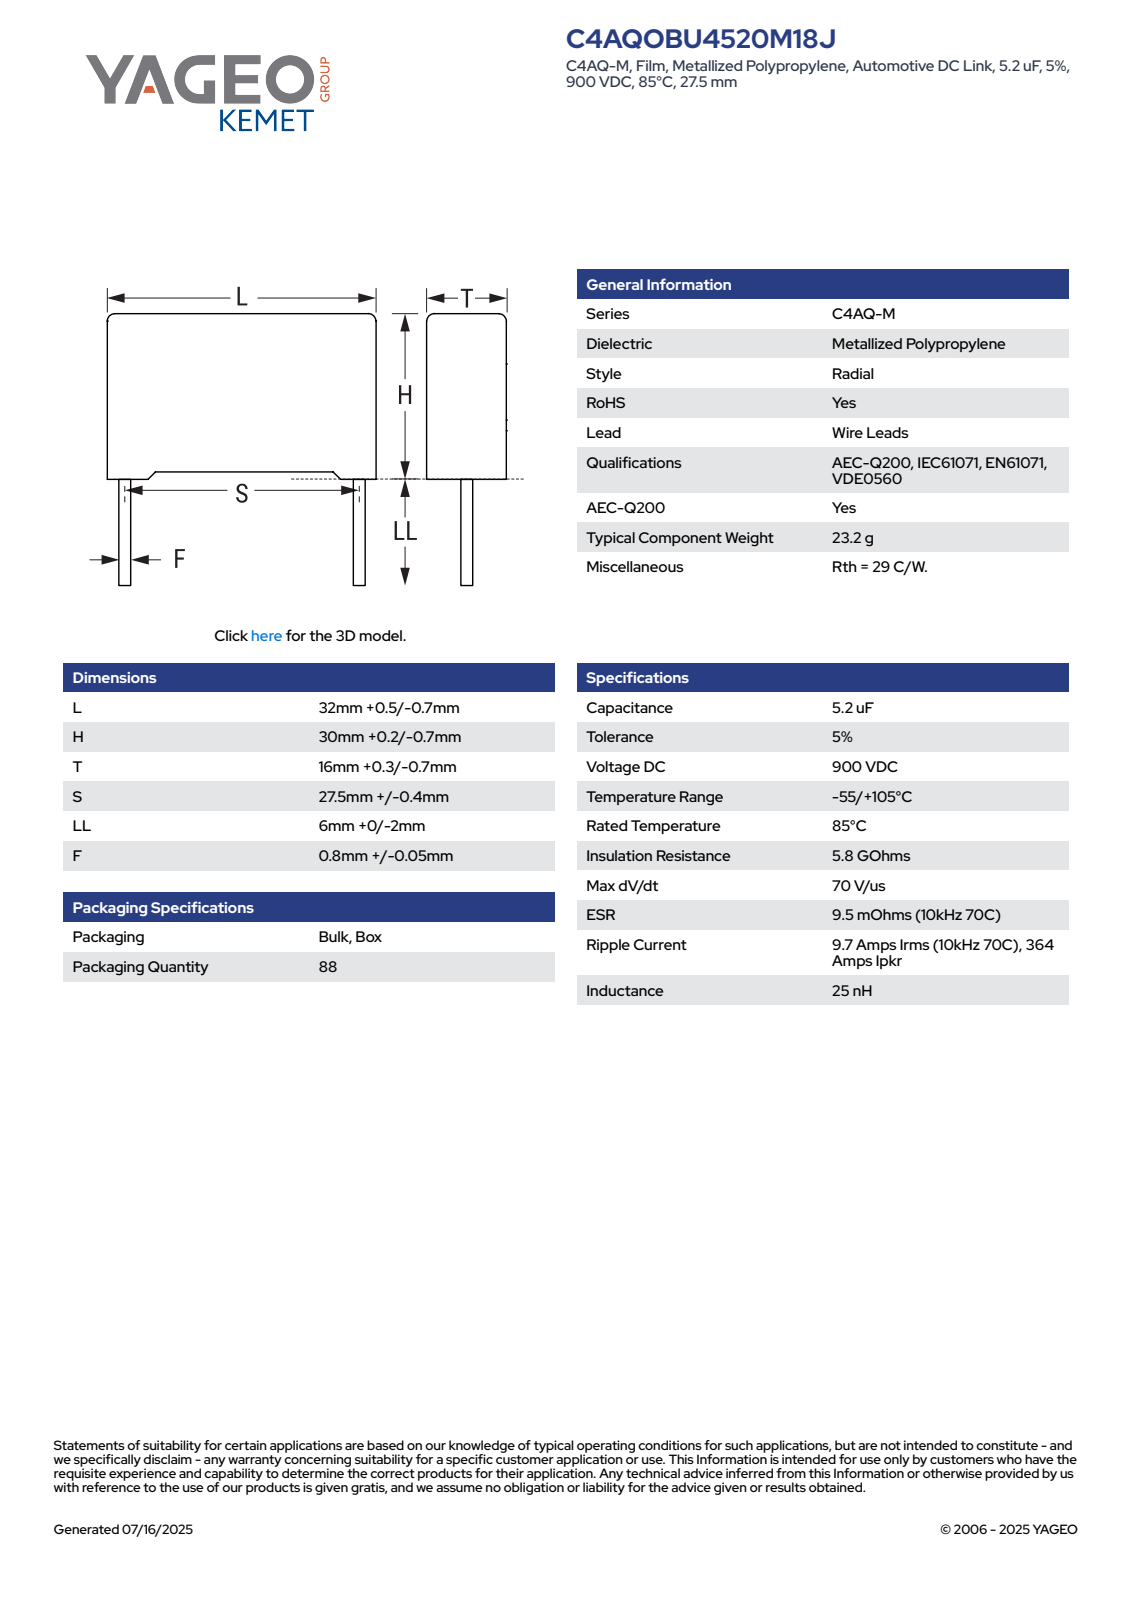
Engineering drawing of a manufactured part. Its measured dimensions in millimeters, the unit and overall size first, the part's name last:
Units: millimetres
Overall size (bounding box): 36.2 × 32.5 × 16.3
Round bosses / shafts (diameter × count): ⌀0.85 ×2
Partial cylindrical surfaces — rounded edges, fillets, slot ends (radius × count): R0.5 ×4
Main face-to-face distances: 16.3, 32.5, 29.16, 29.45, 0.75, 1.04, 30.2, 1.08, 31.42, 16.31
Volume: 15 532 mm³ · Surface area: 4 089 mm²
Bodies: 4 solids, 85 faces (77 planar, 8 cylindrical, 0 other)
Part name (STEP PRODUCT): CFR_RB2CFP_32X30X16_L32.5H30.2T16.3S27.5LL6F0.85
STEP written by: SolidWorks 2014 (AUTOMOTIVE_DESIGN)
